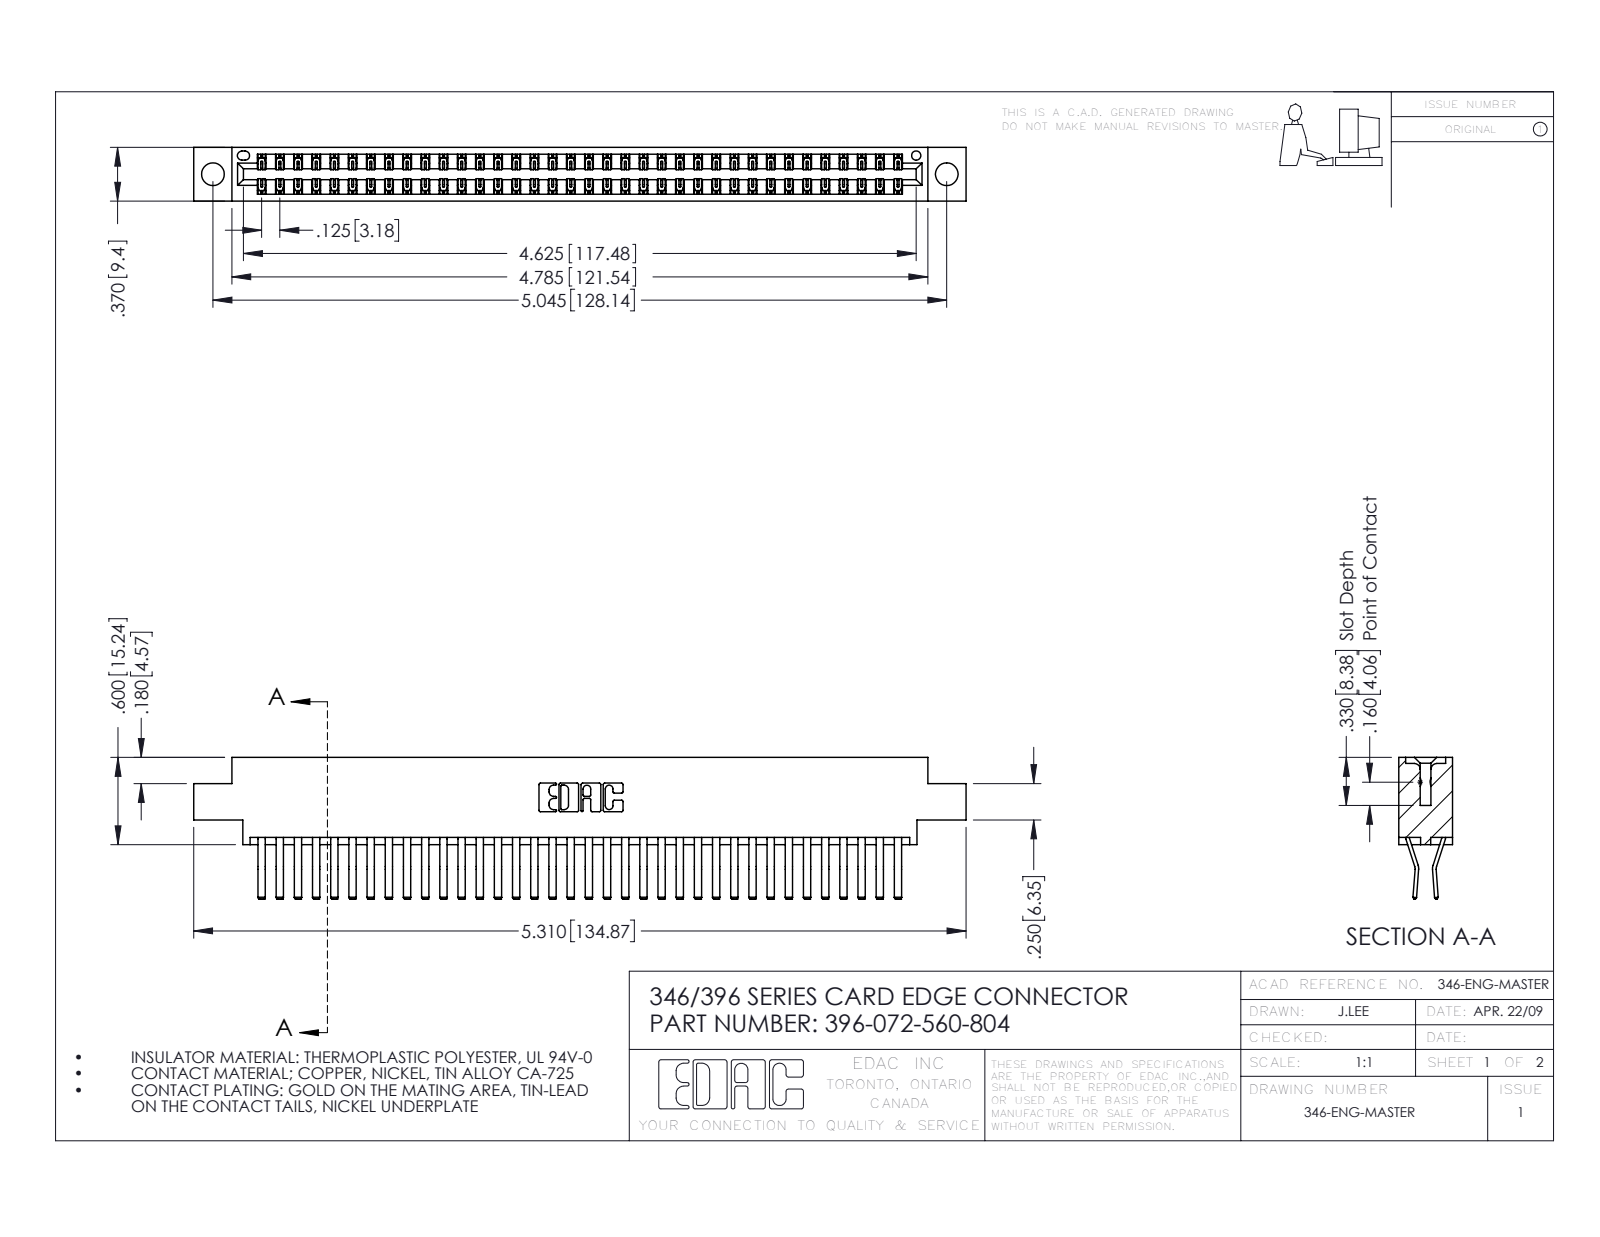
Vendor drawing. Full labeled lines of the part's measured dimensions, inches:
Part name (STEP PRODUCT): 396-072-560-804; 346 Part_0.170 Offset - 0.156 Dia-TH; 345-292-001_560 Tail
STEP written by: SolidWorks 2016 (CONFIG_CONTROL_DESIGN)
Units: inches
Bodies: 73 solids, 4014 faces (2600 planar, 1414 cylindrical, 0 other)
Overall size (bounding box): 5.31 × 0.975 × 0.37
Volume: 0.814 in³ · Surface area: 30.21 in²
Round holes (diameter × count): ⌀0.156 ×2, ⌀0.064 ×1
Partial cylindrical surfaces — rounded edges, fillets, slot ends (radius × count): R0.006 ×108, R0.01 ×22, R0.007 ×6, R0.031 ×6, R0.026 ×3, R0.01 ×2, R0.014 ×2, R0.022 ×2
Main face-to-face distances: 0.048, 0.322, 0.37, 0.025, 0.25, 0.072, 0.298, 0.275, 0.148, 0.222
Hole centre spacings: 0.246, 4.836, 5.045
